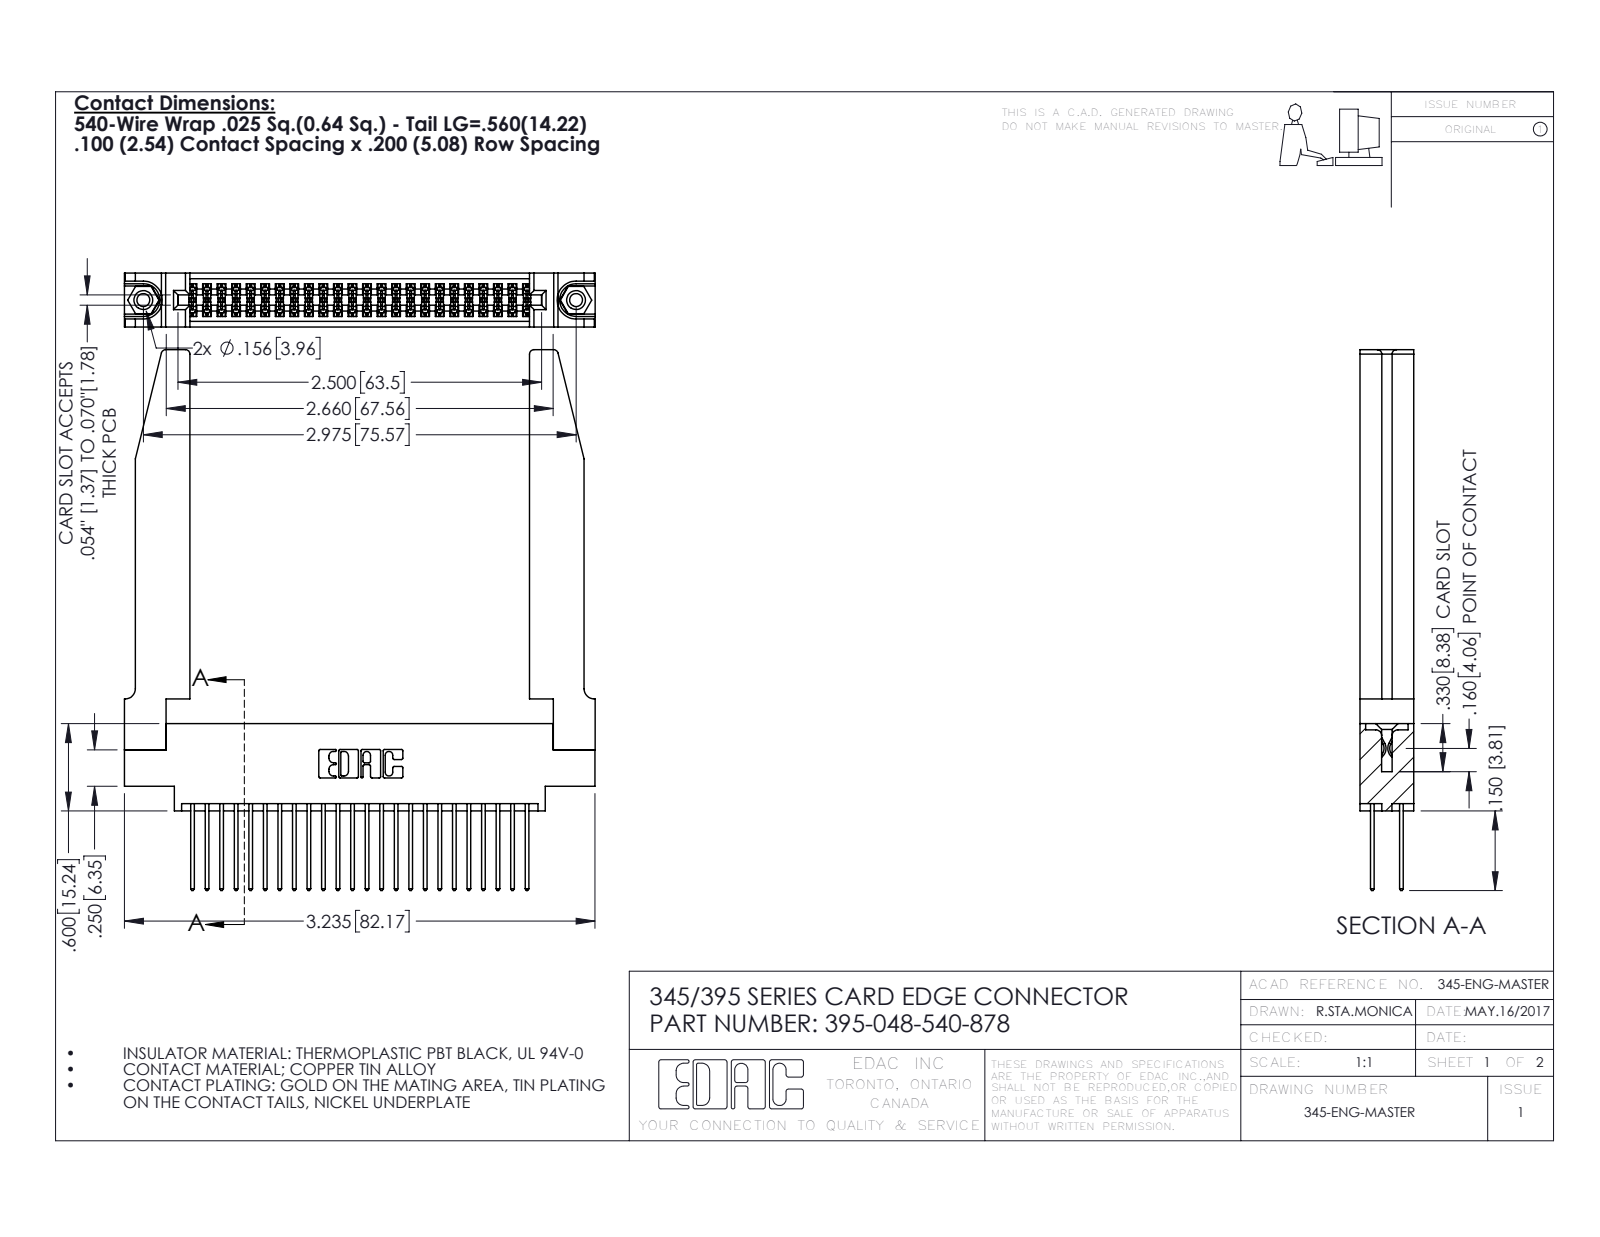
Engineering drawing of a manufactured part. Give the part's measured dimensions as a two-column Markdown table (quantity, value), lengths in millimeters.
| quantity | value |
| --- | --- |
| part name | 345 Part_0.170 Offset - 0.156 Dia-TH; 395-048-540-878; 345-292-001_345-293-140; 345-220-078_345-220-078 (+1 more) |
| STEP written by | SolidWorks 2016 (CONFIG_CONTROL_DESIGN) |
| units | millimeters |
| bodies | 53 solids, 2764 faces (1810 planar, 902 cylindrical, 52 other) |
| overall size | 94.4 × 82.2 × 9.4 |
| volume | 15 600 mm³ |
| surface area | 19 140 mm² |
| round holes (diameter × count) | 2.3 × 2, 3.2 × 2, 4 × 2, 1.6 × 1 |
| round bosses / shafts (diameter × count) | 3.9 × 2 |
| partial cylindrical surfaces (radius × count) | 0.2 × 72, 0.3 × 48, 0.3 × 22, 0.8 × 8, 0.2 × 6, 0.8 × 6, 0.7 × 3, 0.4 × 2 |
| main face-to-face distances | 9.4, 1.8, 7.6, 2.5, 6.9, 0.6, 5.1, 5.7, 4.4, 3.8 |
| hole center spacings | 6.9, 69.6, 75.6 |
